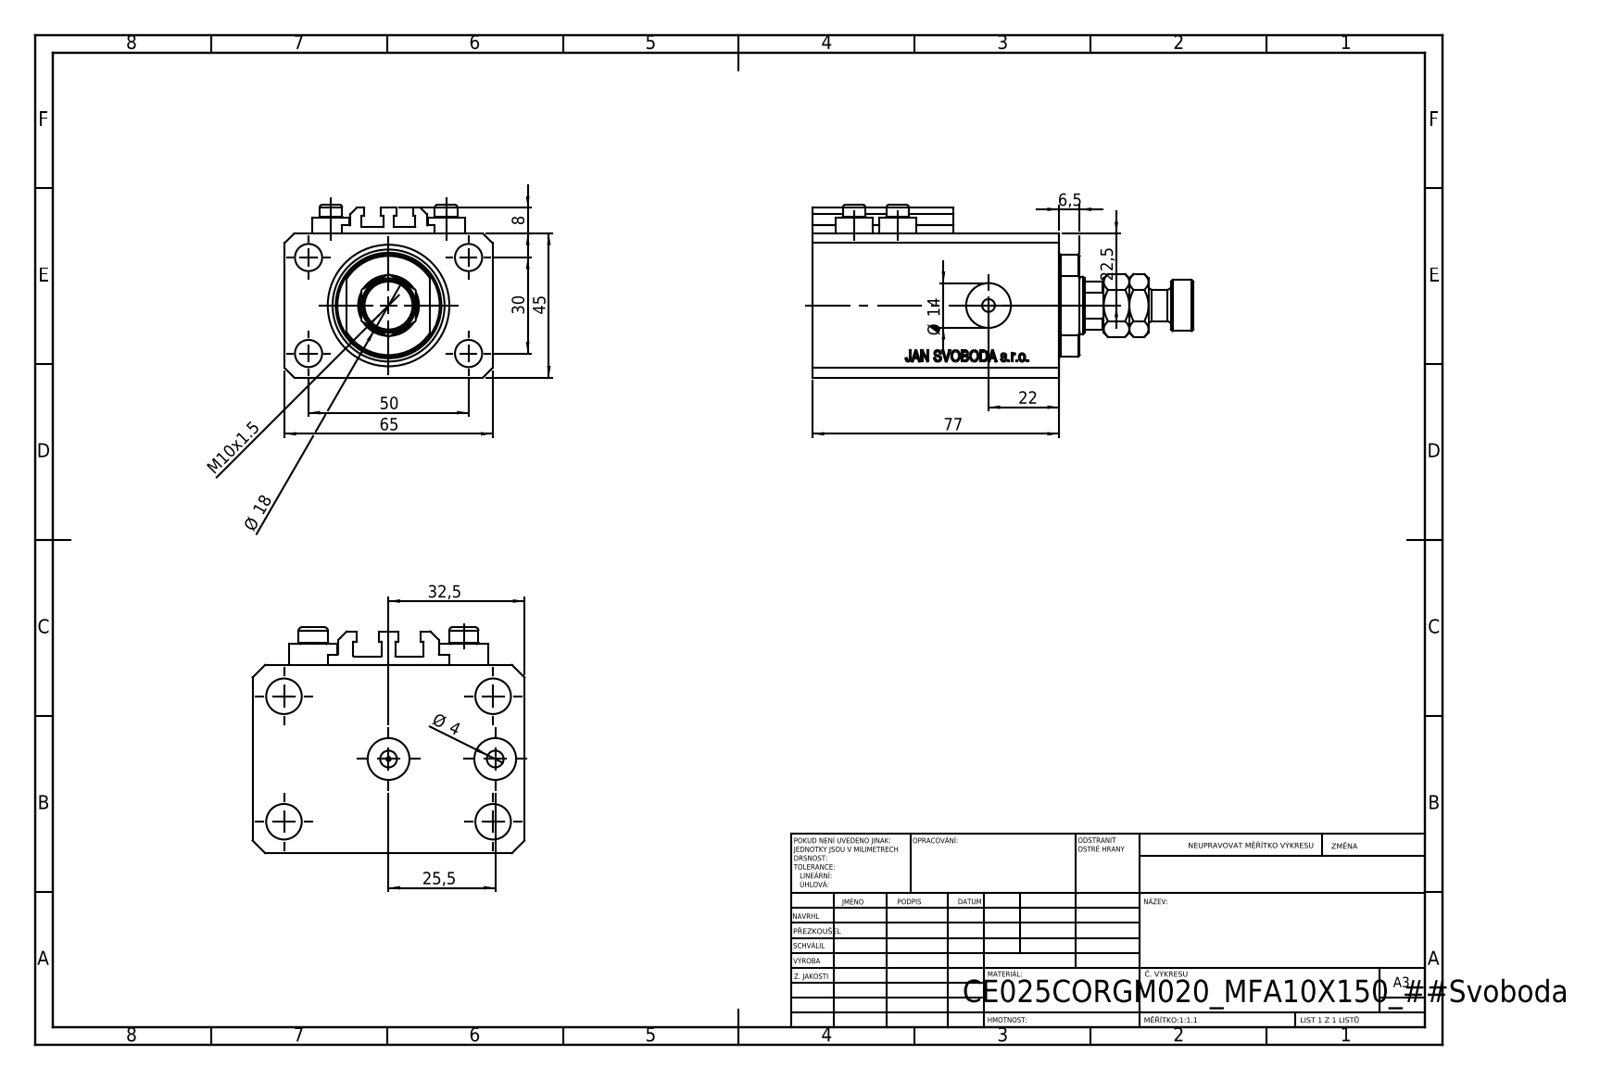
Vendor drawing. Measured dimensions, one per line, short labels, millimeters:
name: ALLEN BOLT V250CE; MFA; V250CE_VC_C; V250CE_C_VCP (+1 more)
written by: SolidWorks 2019 (CONFIG_CONTROL_DESIGN)
unit: mm
bodies: 9 solids, 1094 faces (520 planar, 96 cylindrical, 478 other)
size: 119 × 65 × 54
volume: 216 927 mm³; area: 59 745 mm²
holes: 8× ⌀4, 5× ⌀8.5, 2× ⌀10, 2× ⌀14, 1× ⌀1.25, 1× ⌀18, 1× ⌀25, 1× ⌀38
bosses: 4× ⌀11.6, 4× ⌀7, 1× ⌀16
rounds: 10× R0.2, 1× R8.5, 1× R16
face distances: 45, 65, 14, 77, 63, 6.9, 56.1, 70.1, 20.5, 3
hole spacings: 29.15, 13.6, 15.01, 30, 36, 38.48, 50, 52.68
